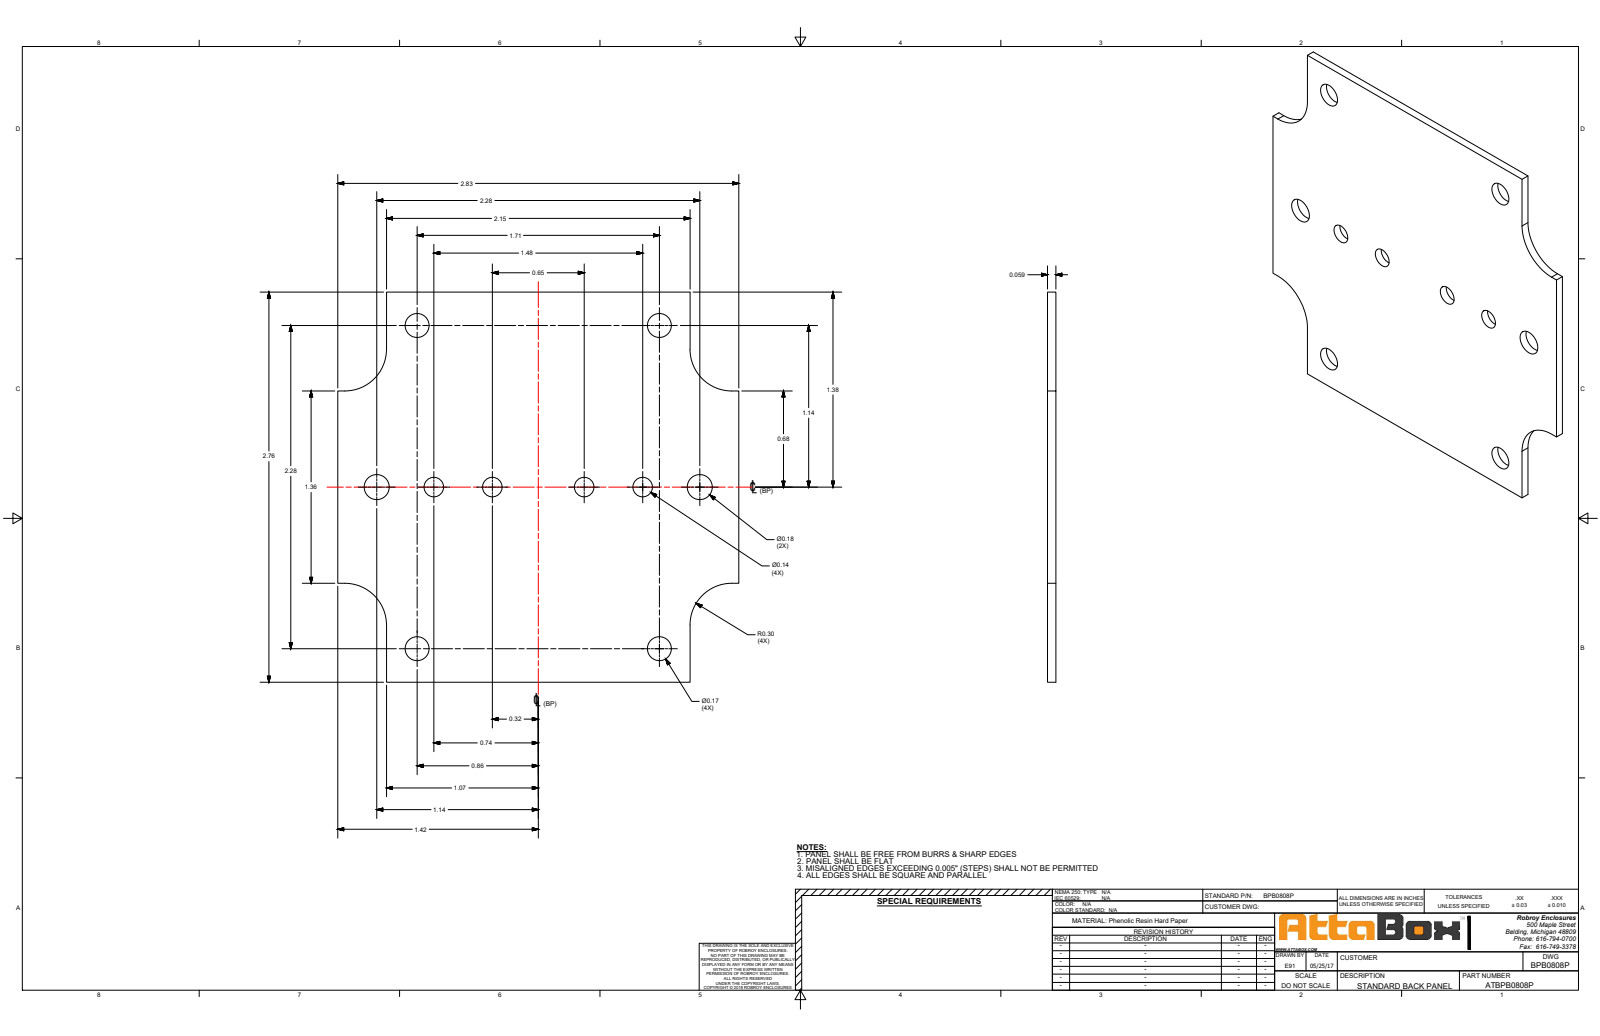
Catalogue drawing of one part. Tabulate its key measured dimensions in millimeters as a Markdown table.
| quantity | value |
| --- | --- |
| part name | BPB0808P |
| STEP written by | SolidWorks 2018 (AUTOMOTIVE_DESIGN) |
| units | millimeters |
| bodies | 1 solid, 28 faces (14 planar, 14 cylindrical, 0 other) |
| overall size | 72 × 70 × 1.5 |
| volume | 6 510 mm³ |
| surface area | 9 271 mm² |
| round holes (diameter × count) | 3.5 × 4, 4.3 × 4, 4.5 × 2 |
| partial cylindrical surfaces (radius × count) | 7.5 × 4 |
| main face-to-face distances | 1.5, 70, 8.7, 63.2, 72, 54.5, 17.8, 52.2, 34.5 |
| hole center spacings | 29.2, 29.9, 32, 41.7, 49.8, 58.4, 58, 10.3 |
